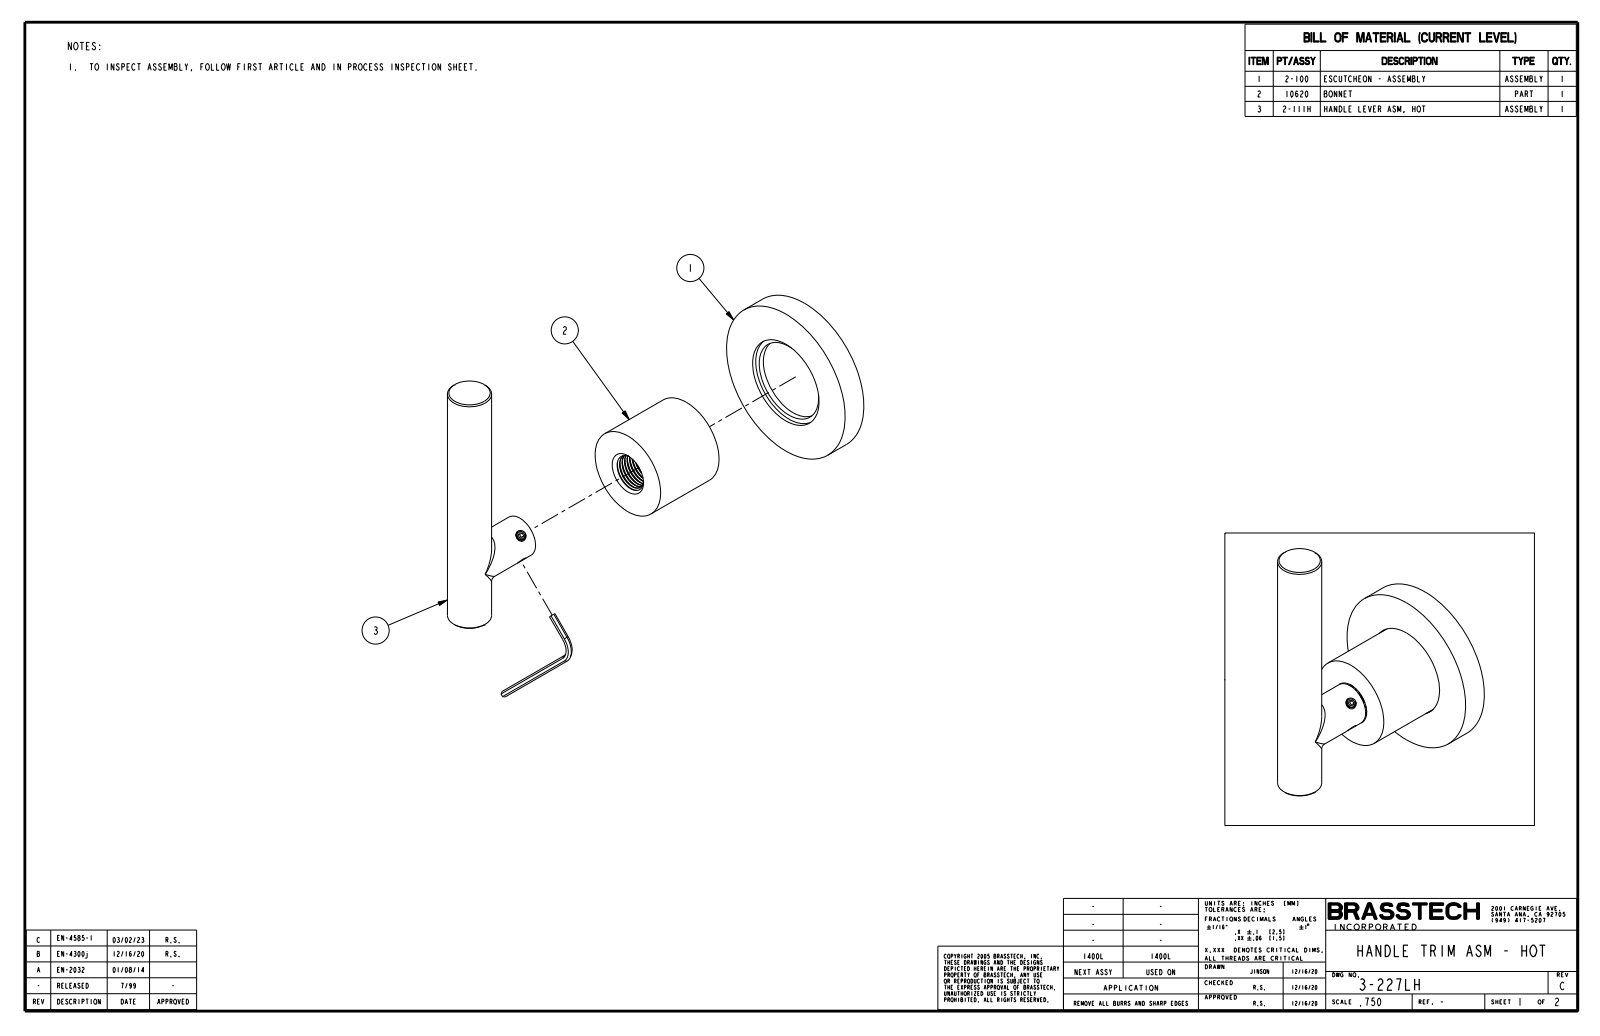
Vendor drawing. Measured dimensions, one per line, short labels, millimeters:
name: 3-227LH
written by: CREO PARAMETRIC BY PTC INC, 2018400 (CONFIG_CONTROL_DESIGN)
unit: mm
bodies: 1 solid, 22 faces (5 planar, 9 cylindrical, 8 other)
size: 106.1 × 71.8 × 60.3
volume: 75 120 mm³; area: 16 330 mm²
bosses: 2× ⌀15.9, 1× ⌀60.3, 1× ⌀33.4
face distances: 9.5, 37.7, 28.1, 98.4
